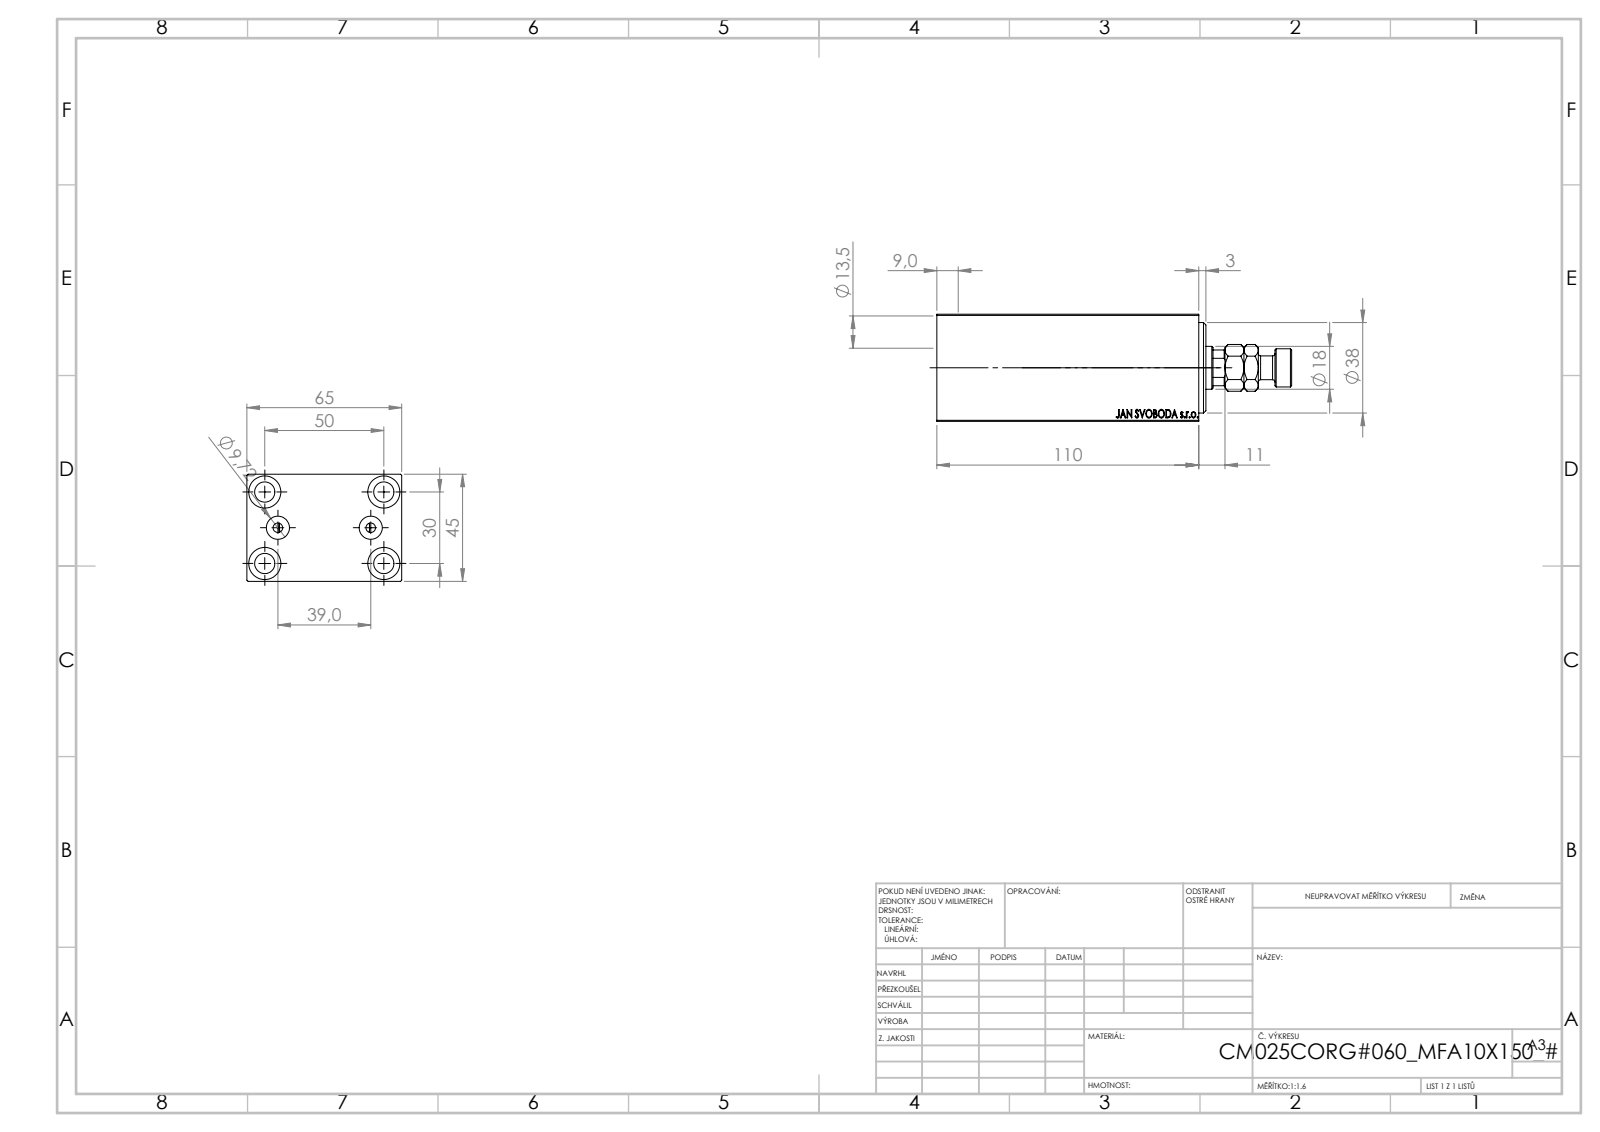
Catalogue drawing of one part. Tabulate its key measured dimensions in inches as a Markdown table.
| quantity | value |
| --- | --- |
| part name | MFA; V450CM_C_VCP; V450CM_C_Body; V450CM_VC_B |
| STEP written by | SolidWorks 2019 (CONFIG_CONTROL_DESIGN) |
| units | inches |
| bodies | 4 solids, 910 faces (424 planar, 60 cylindrical, 426 other) |
| overall size | 5.866 × 2.559 × 1.772 |
| volume | 17.2 in³ |
| surface area | 106 in² |
| round holes (diameter × count) | 0.335 × 5, 0.531 × 4, 0.157 × 2, 0.383 × 2, 0.709 × 1, 0.846 × 1, 0.984 × 1, 1.063 × 1, 1.496 × 1 |
| round bosses / shafts (diameter × count) | 0.63 × 1, 0.394 × 1 |
| partial cylindrical surfaces (radius × count) | 0.335 × 1 |
| main face-to-face distances | 1.772, 2.559, 0.236, 3.898, 4.094, 4.331, 4.134, 0.197, 0.118, 0.315 |
| hole center spacings | 0.629, 1.148, 1.849, 0.768, 1.181, 1.969, 2.296, 1.535 |
